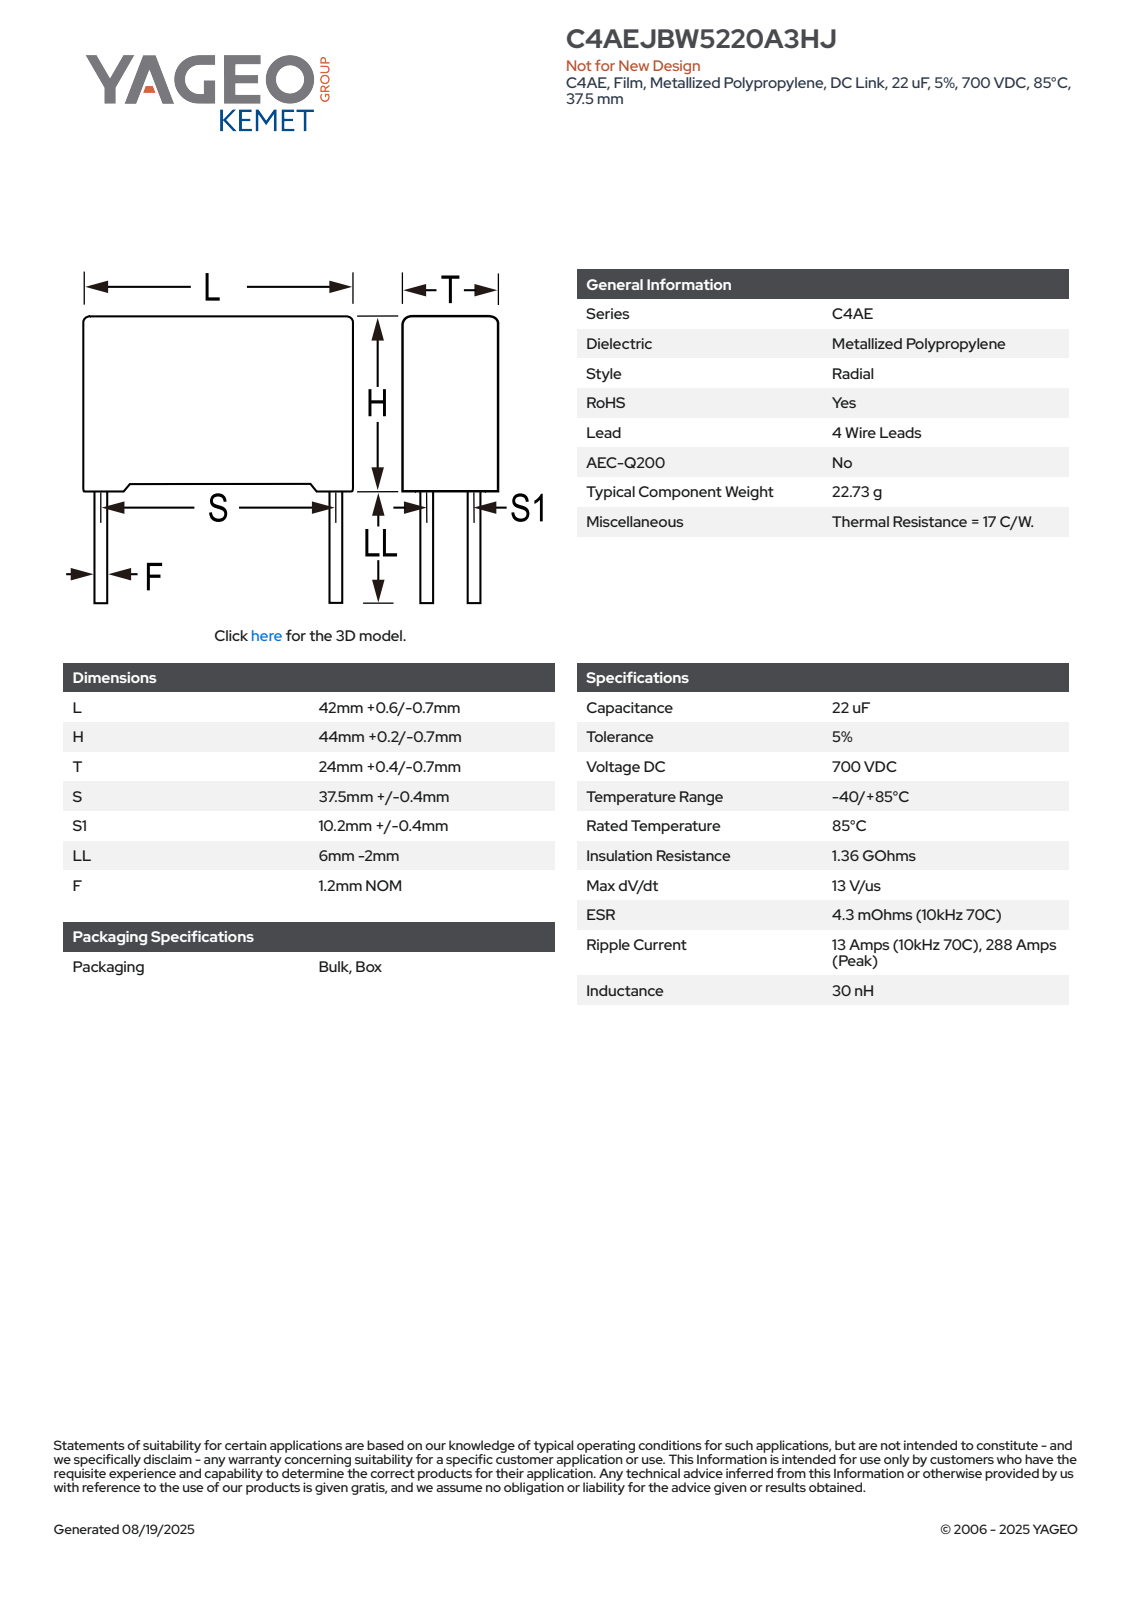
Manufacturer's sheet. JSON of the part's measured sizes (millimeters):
{"part_name": "CFP_RB4_42X44X24_L42.6H44.2T24.4S37.5S110.2LL4F1.2", "step_written_by": "SolidWorks 2014 (AUTOMOTIVE_DESIGN)", "units": "millimeters", "bodies": {"solids": 4, "faces": 87, "planar": 79, "cylindrical": 8, "other": 0}, "overall_size": [48.2, 42.6, 24.41], "volume_mm3": 44758, "surface_area_mm2": 8217, "round_bosses_or_shafts": [[1.2, 4]], "face_to_face_distances": [24.4, 42.6, 42.9, 1.3, 44.2, 1.5, 24.41, 41.1, 22.9, 39.6]}
